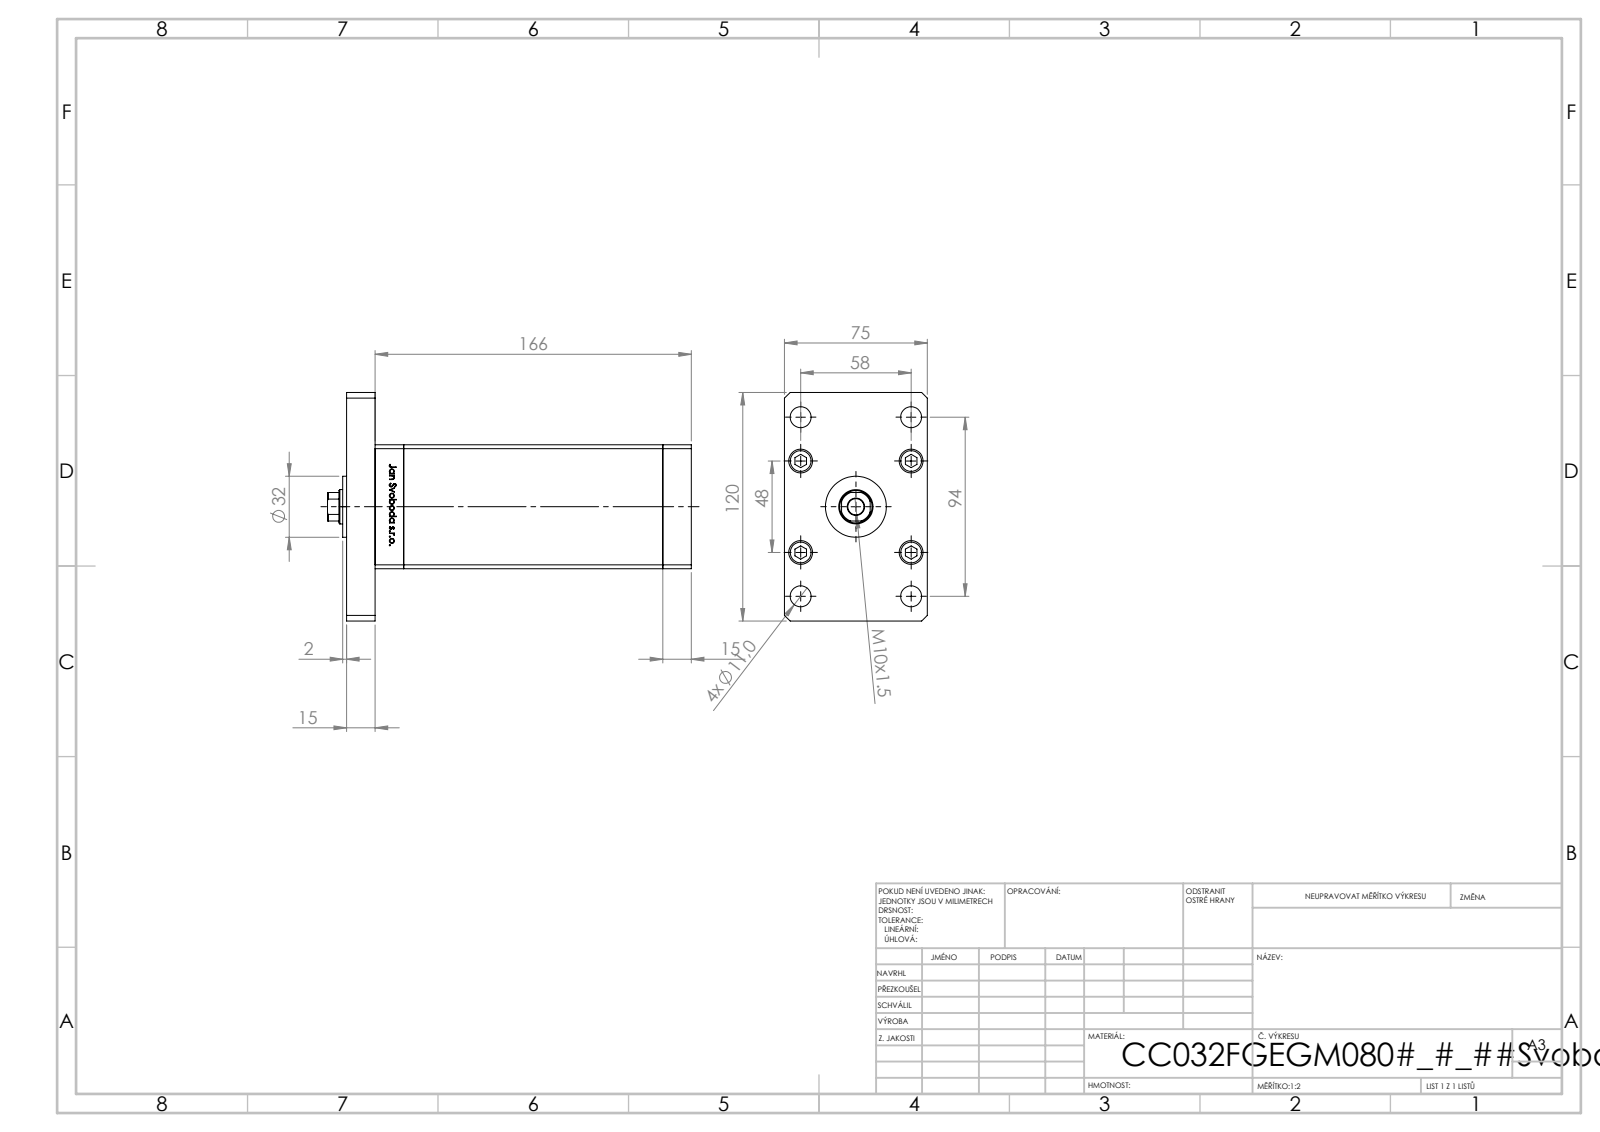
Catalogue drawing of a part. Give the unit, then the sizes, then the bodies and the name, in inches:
Units: inches
Overall size (bounding box): 7.52 × 4.724 × 2.953
Round holes (diameter × count): ⌀0.354 ×5, ⌀0.531 ×5, ⌀0.315 ×4, ⌀0.433 ×4, ⌀0.492 ×4, ⌀0.079 ×2, ⌀0.518 ×2, ⌀0.335 ×1, ⌀0.709 ×1, ⌀0.768 ×1
Round bosses / shafts (diameter × count): ⌀0.492 ×5, ⌀0.315 ×5, ⌀1.26 ×1
Partial cylindrical surfaces — rounded edges, fillets, slot ends (radius × count): R0.037 ×2, R0.335 ×1
Main face-to-face distances: 0.591, 2.953, 5.945, 6.535, 2.559, 1.181, 5.354, 7.126, 0.512, 6.024
Hole centre spacings: 0.945, 0.906, 1.482, 2.174, 2.283, 2.456, 2.795, 3.609
Volume: 51.78 in³ · Surface area: 247.9 in²
Bodies: 19 solids, 1308 faces (515 planar, 187 cylindrical, 606 other)
Part name (STEP PRODUCT): V220C_F_MIDDLE; V220C BACK_F; ALLEN BOLT; V220C_VC_F (+2 more)
STEP written by: SolidWorks 2019 (CONFIG_CONTROL_DESIGN)
